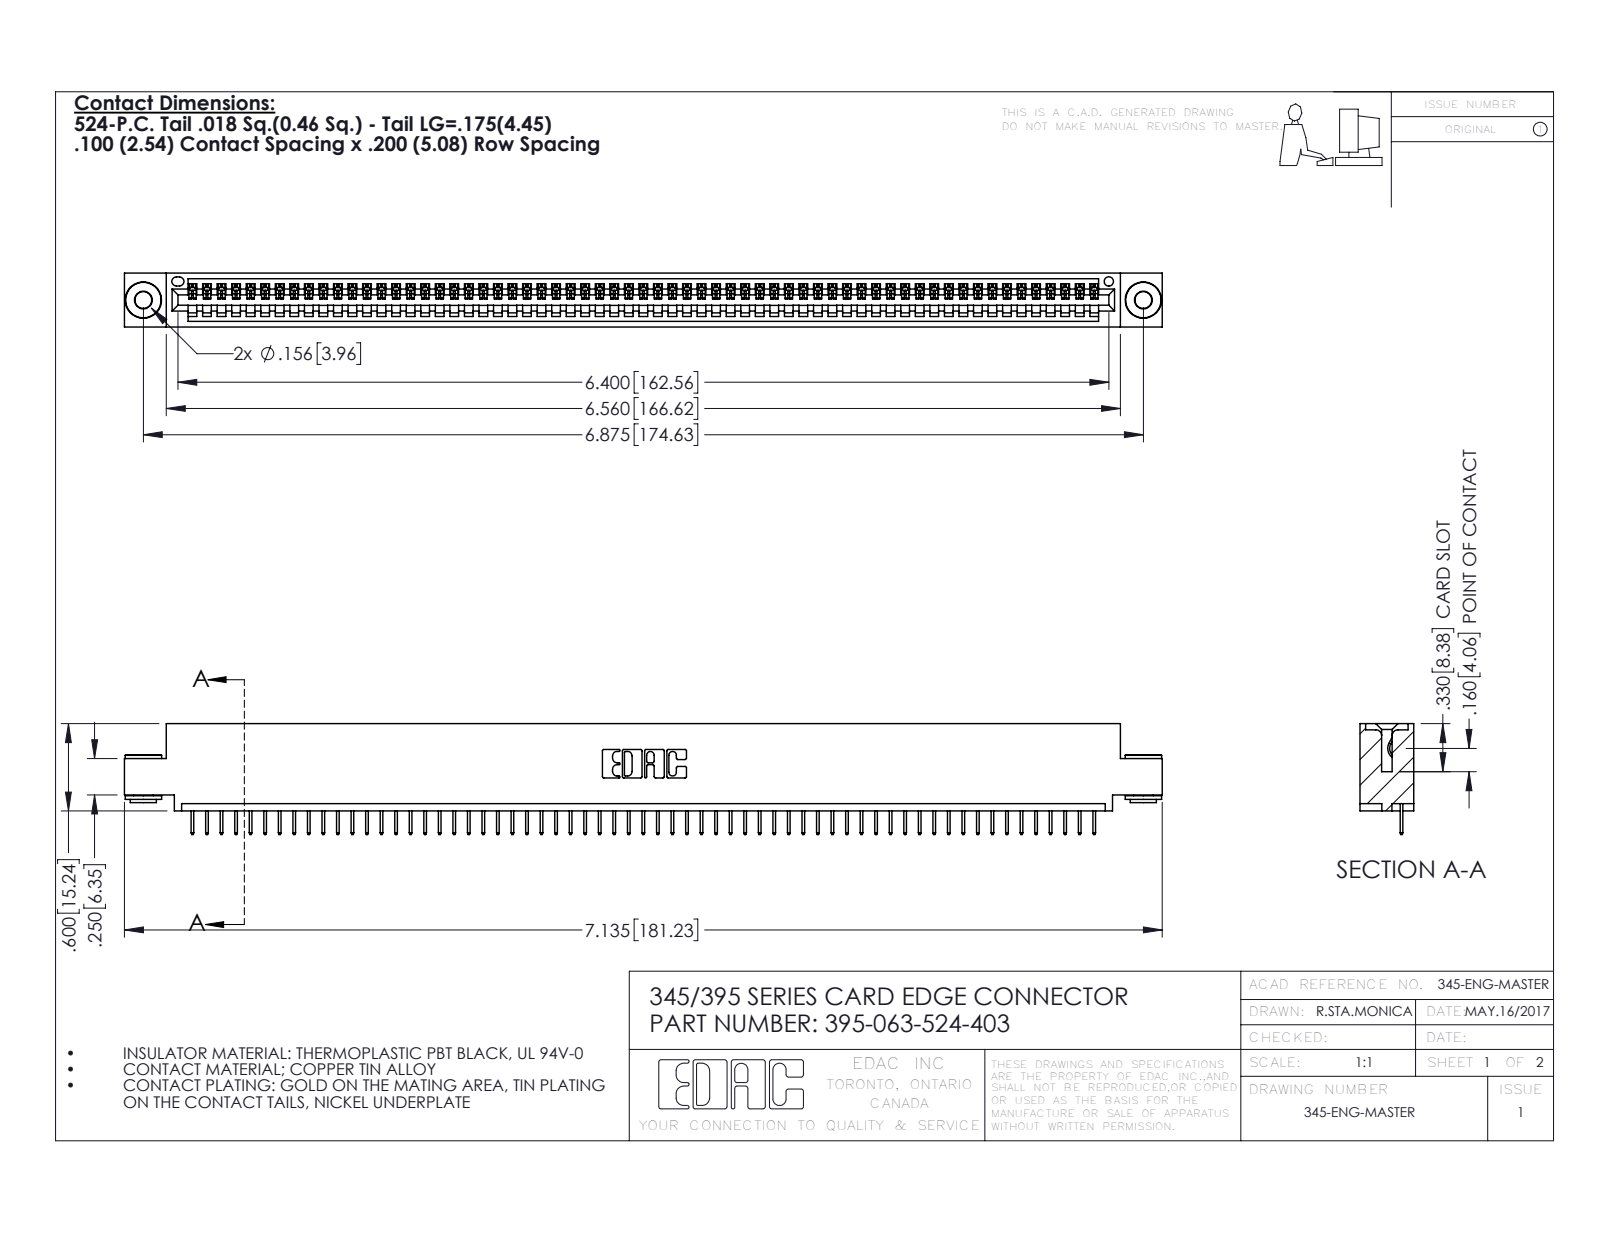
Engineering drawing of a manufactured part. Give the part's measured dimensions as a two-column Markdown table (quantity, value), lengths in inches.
| quantity | value |
| --- | --- |
| part name | 345 Part_0.110 Offset - 0.156 Dia-TH; 345-292-001_345-293-124; 345-250-002_345-250-002-102; 395-063-524-403 |
| STEP written by | SolidWorks 2016 (CONFIG_CONTROL_DESIGN) |
| units | inches |
| bodies | 66 solids, 4074 faces (2992 planar, 1074 cylindrical, 8 other) |
| overall size | 7.135 × 0.762 × 0.37 |
| volume | 1.042 in³ |
| surface area | 34.86 in² |
| round holes (diameter × count) | 0.116 × 2, 0.156 × 2, 0.064 × 1 |
| round bosses / shafts (diameter × count) | 0.25 × 2, 0.18 × 2, 0.136 × 2 |
| partial cylindrical surfaces (radius × count) | 0.006 × 126, 0.01 × 22, 0.007 × 6, 0.031 × 6, 0.026 × 3, 0.031 × 2, 0.04 × 2, 0.014 × 1 |
| main face-to-face distances | 0.072, 0.298, 0.37, 0.2, 0.025, 0.098, 0.272, 0.225, 0.072, 0.149 |
| hole center spacings | 0.27, 6.639, 6.875 |
